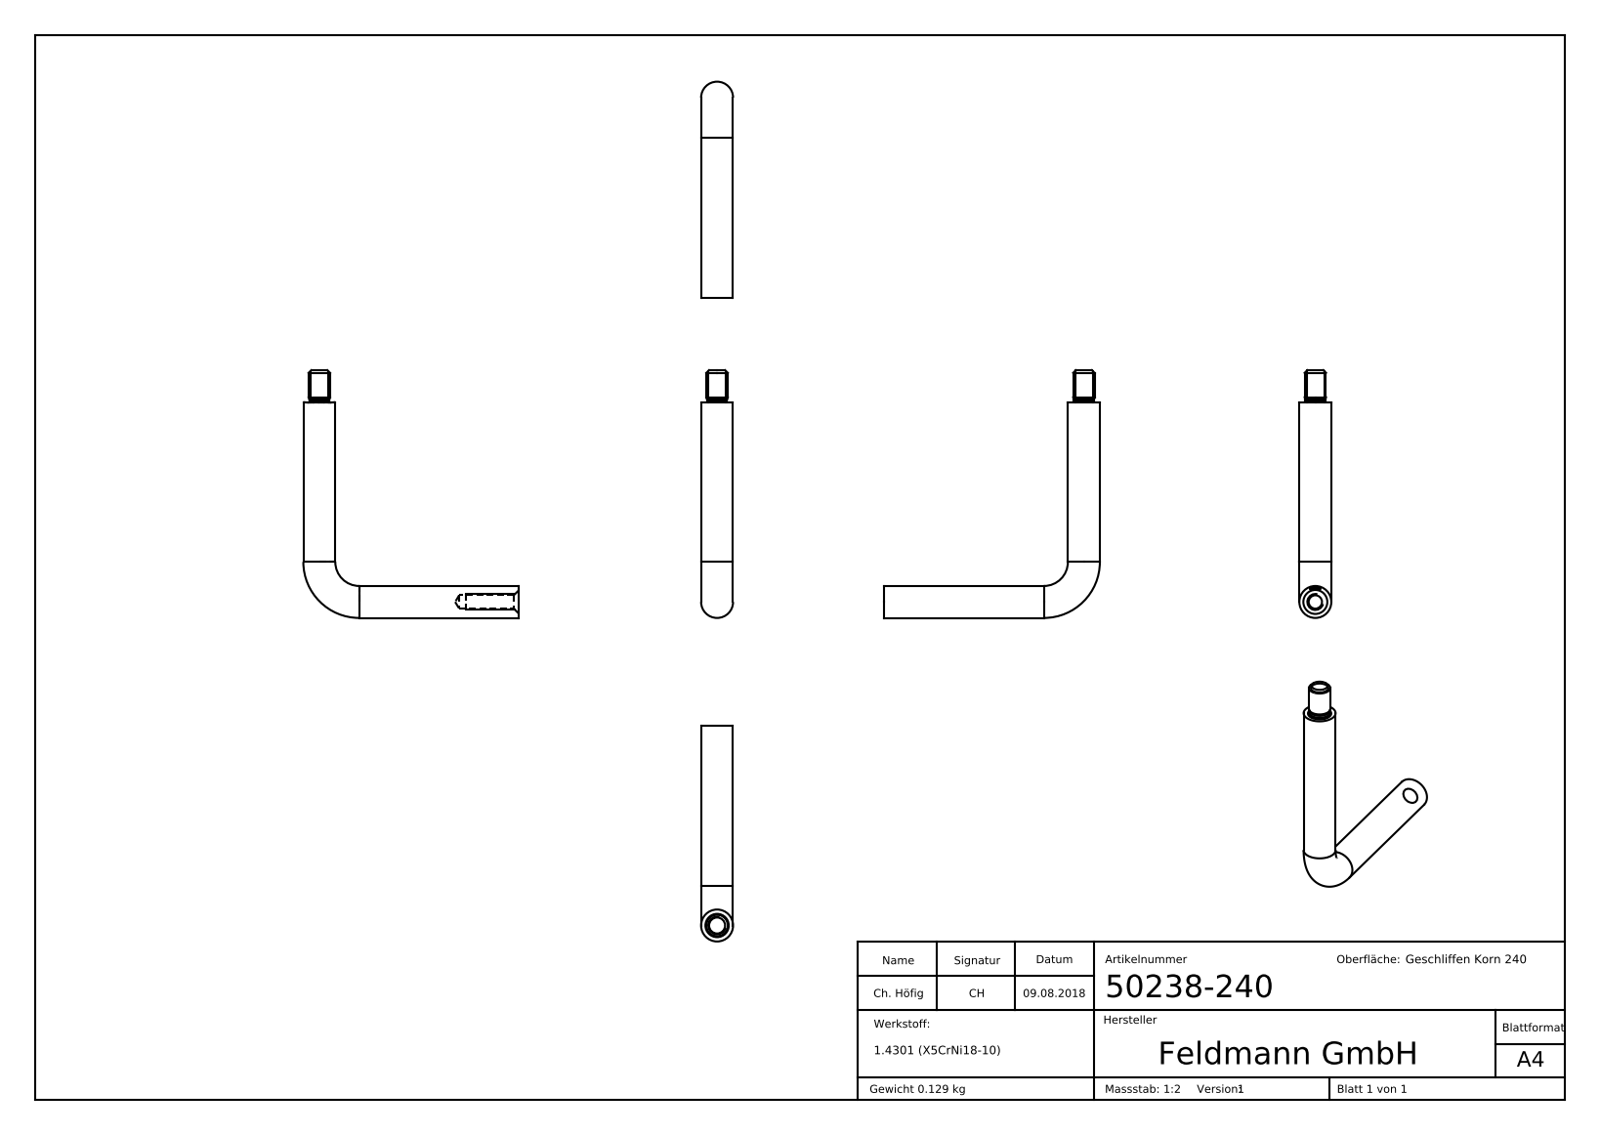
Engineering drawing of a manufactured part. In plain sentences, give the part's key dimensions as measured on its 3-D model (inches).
The part is named "50238-240". Its 3-D file was written by "SolidWorks 2015 (CONFIG_CONTROL_DESIGN)". It is 1 solid with 262 faces: 119 planar, 10 cylindrical and 133 other. Overall it measures 3.661 by 3.189 by 0.472 inches. Its volume is 0.996 cubic inches and its surface area 9.723 square inches. Round holes: 1 of diameter 0.197. Round bosses or shafts: 2 of diameter 0.472, 1 of diameter 0.315, 1 of diameter 0.299.
